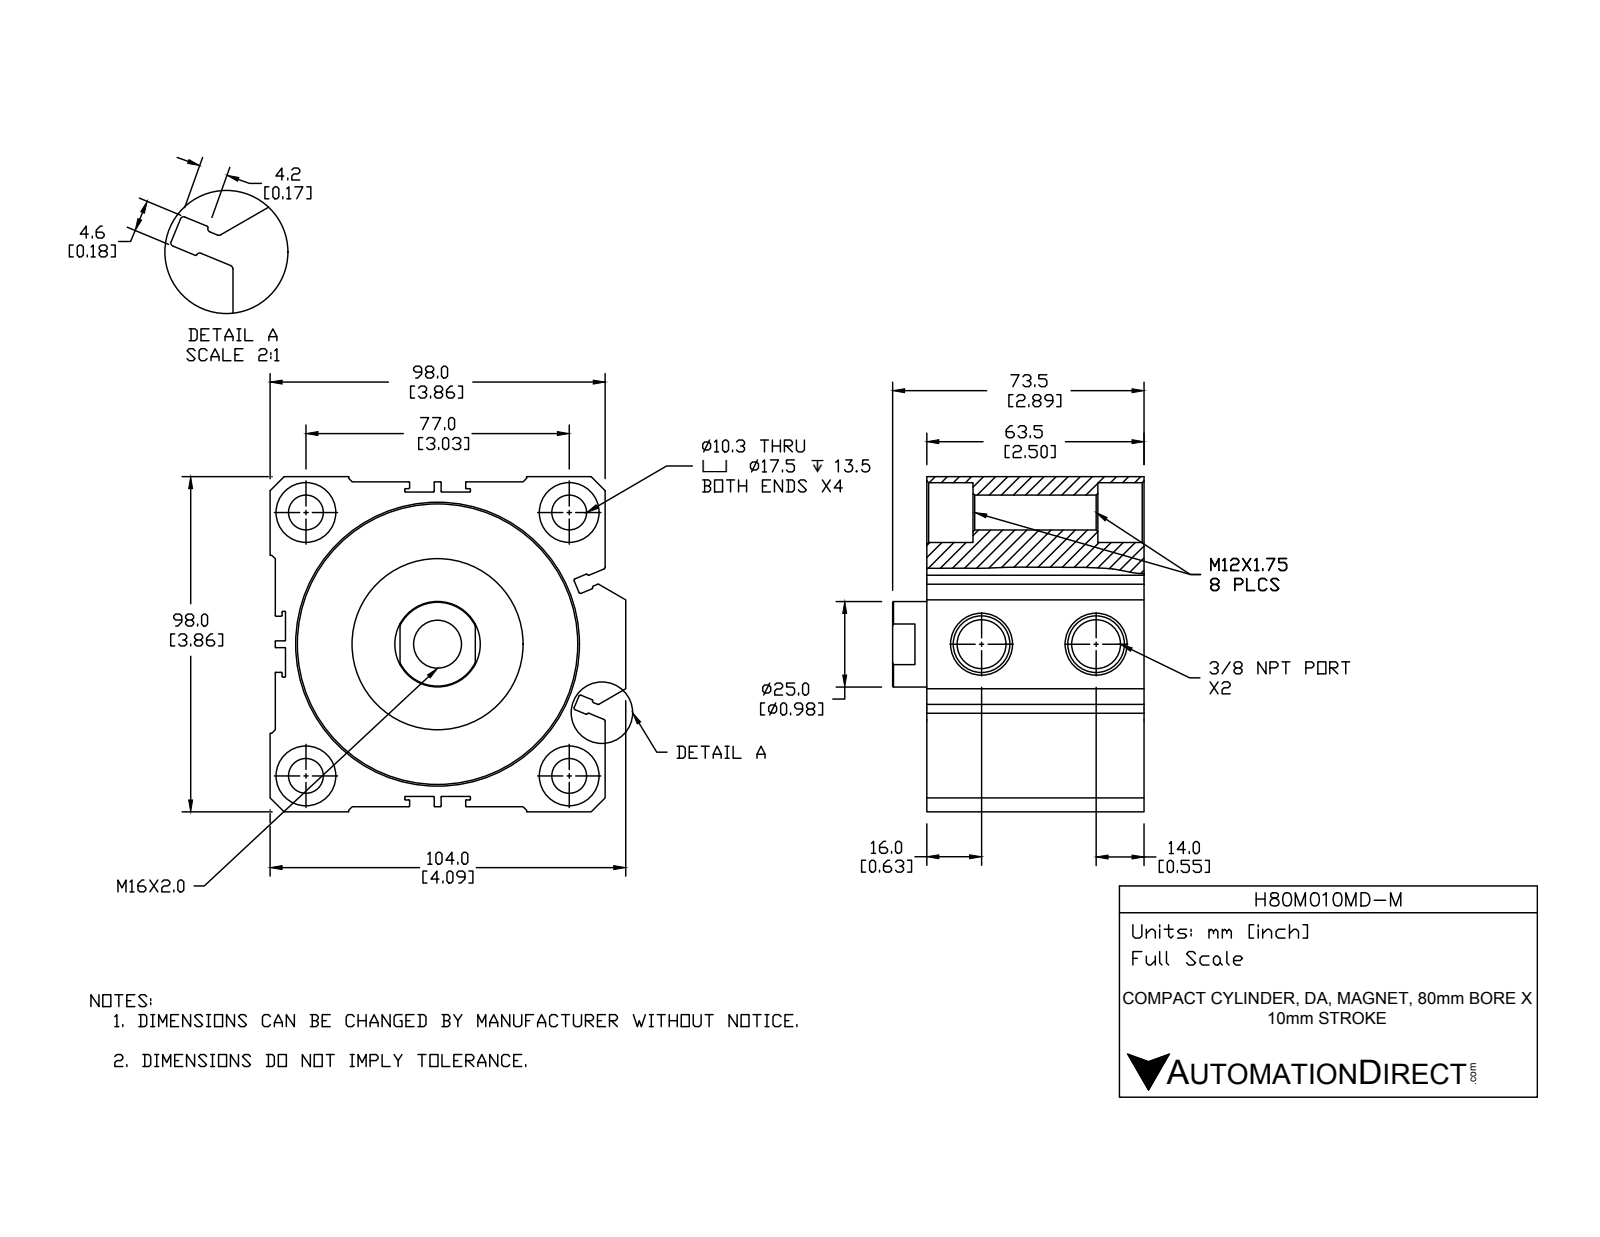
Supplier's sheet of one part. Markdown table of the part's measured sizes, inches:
| quantity | value |
| --- | --- |
| part name | H80M010MD-M-PISTON; H80M010MD-M; H80M010MD-M-BODY |
| STEP written by | SolidWorks 2015 (CONFIG_CONTROL_DESIGN) |
| units | inches |
| bodies | 2 solids, 261 faces (105 planar, 103 cylindrical, 53 other) |
| overall size | 4.094 × 3.858 × 2.894 |
| volume | 28.75 in³ |
| surface area | 160.4 in² |
| round holes (diameter × count) | 0.402 × 4, 0.689 × 4, 0.562 × 2, 0.551 × 1, 0.984 × 1, 1.792 × 1, 3.15 × 1, 3.228 × 1 |
| round bosses / shafts (diameter × count) | 1.969 × 1, 1.535 × 1 |
| partial cylindrical surfaces (radius × count) | 0.008 × 40, 0.02 × 12 |
| main face-to-face distances | 0.394, 0.059, 3.799, 3.858, 0.354, 1.421, 1.067, 1.815, 1.461, 0.079 |
| hole center spacings | 2.144, 3.031, 4.287, 1.319 |
